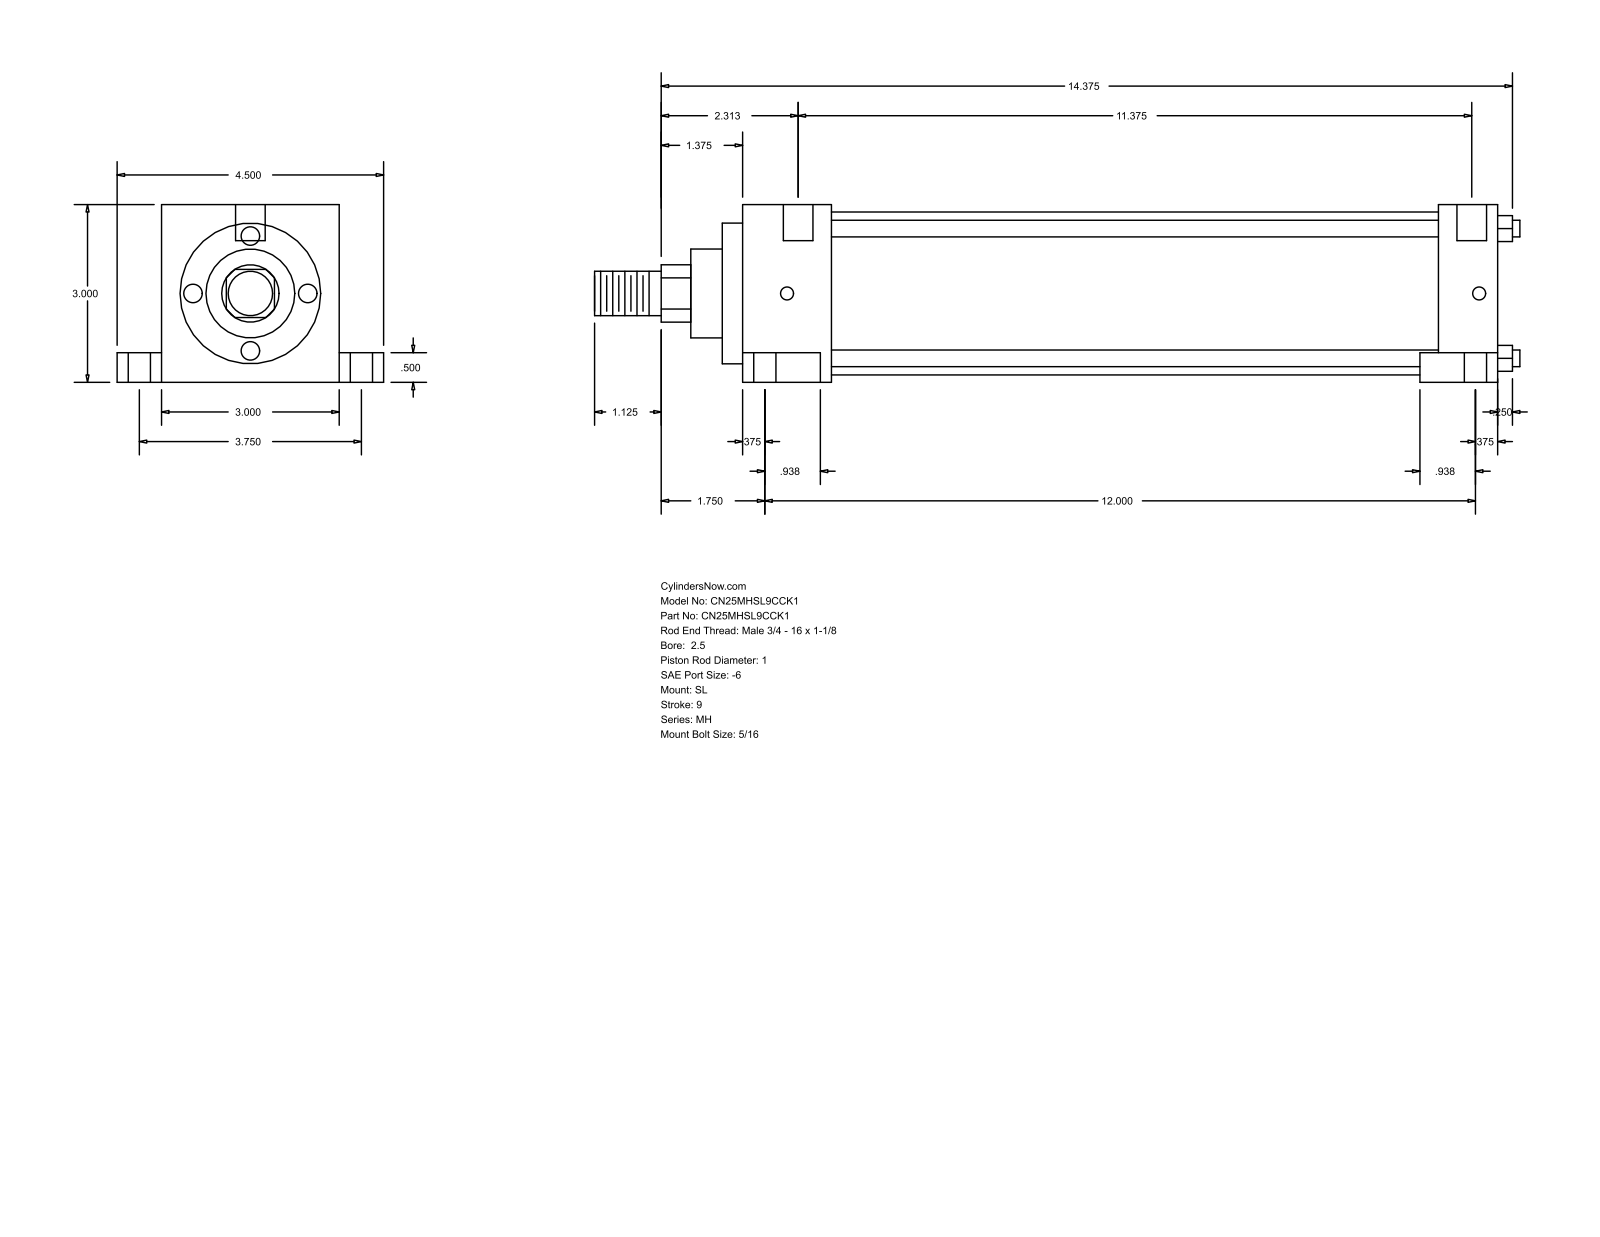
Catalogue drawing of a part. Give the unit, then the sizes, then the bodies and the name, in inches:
Units: inches
Overall size (bounding box): 15.625 × 4.5 × 3
Round holes (diameter × count): ⌀0.219 ×2, ⌀0.375 ×2, ⌀0.625 ×2, ⌀0.5 ×1
Round bosses / shafts (diameter × count): ⌀0.281 ×4, ⌀2.75 ×1, ⌀2.375 ×1, ⌀1.5 ×1, ⌀1 ×1, ⌀0.75 ×1
Partial cylindrical surfaces — rounded edges, fillets, slot ends (radius × count): R0.484 ×1
Main face-to-face distances: 3, 1, 12.094, 13.094, 0.5, 2.5, 0.75, 3.75, 0.531, 12.625
Hole centre spacings: 1.876, 0.125, 3.75
Bodies: 0 solids, 86 faces (61 planar, 25 cylindrical, 0 other)
Part name (STEP PRODUCT): MH_SL__0250_1
STEP written by: GSSL Pune (CONFIG_CONTROL_DESIGN)
